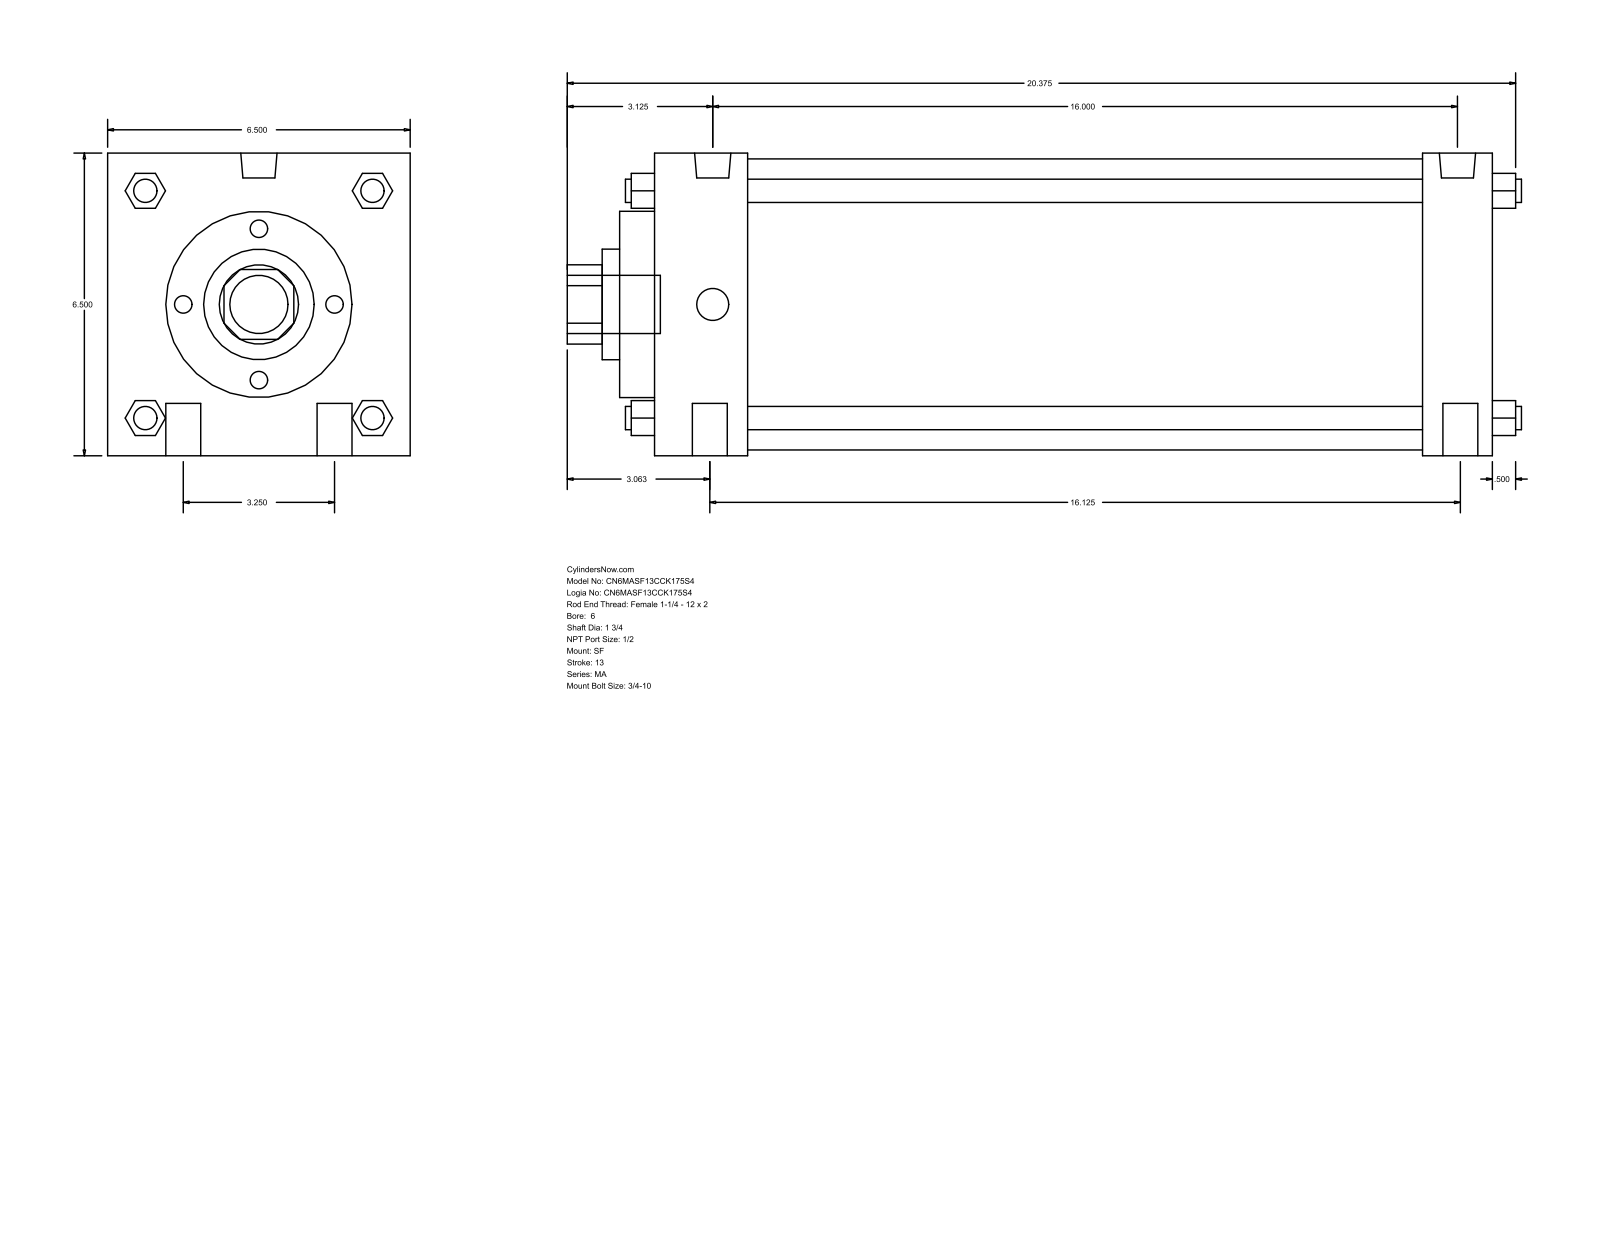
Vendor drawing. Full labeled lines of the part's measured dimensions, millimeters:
Part name (STEP PRODUCT): MA_SF__0600_1.75
STEP written by: GSSL Pune (CONFIG_CONTROL_DESIGN)
Units: millimetres
Bodies: 0 solids, 126 faces (95 planar, 31 cylindrical, 0 other)
Overall size (bounding box): 520.7 × 165.1 × 165.1
Round holes (diameter × count): ⌀44.45 ×1, ⌀60.33 ×1, ⌀101.6 ×1, ⌀158.75 ×1
Round bosses / shafts (diameter × count): ⌀19.05 ×4, ⌀12.7 ×4, ⌀19.77 ×2, ⌀17.46 ×2, ⌀31.75 ×1
Partial cylindrical surfaces — rounded edges, fillets, slot ends (radius × count): R21.63 ×1
Main face-to-face distances: 165.1, 457.2, 19.05, 50.8, 419.11, 38.09, 368.31, 406.4, 69.85, 438.16
